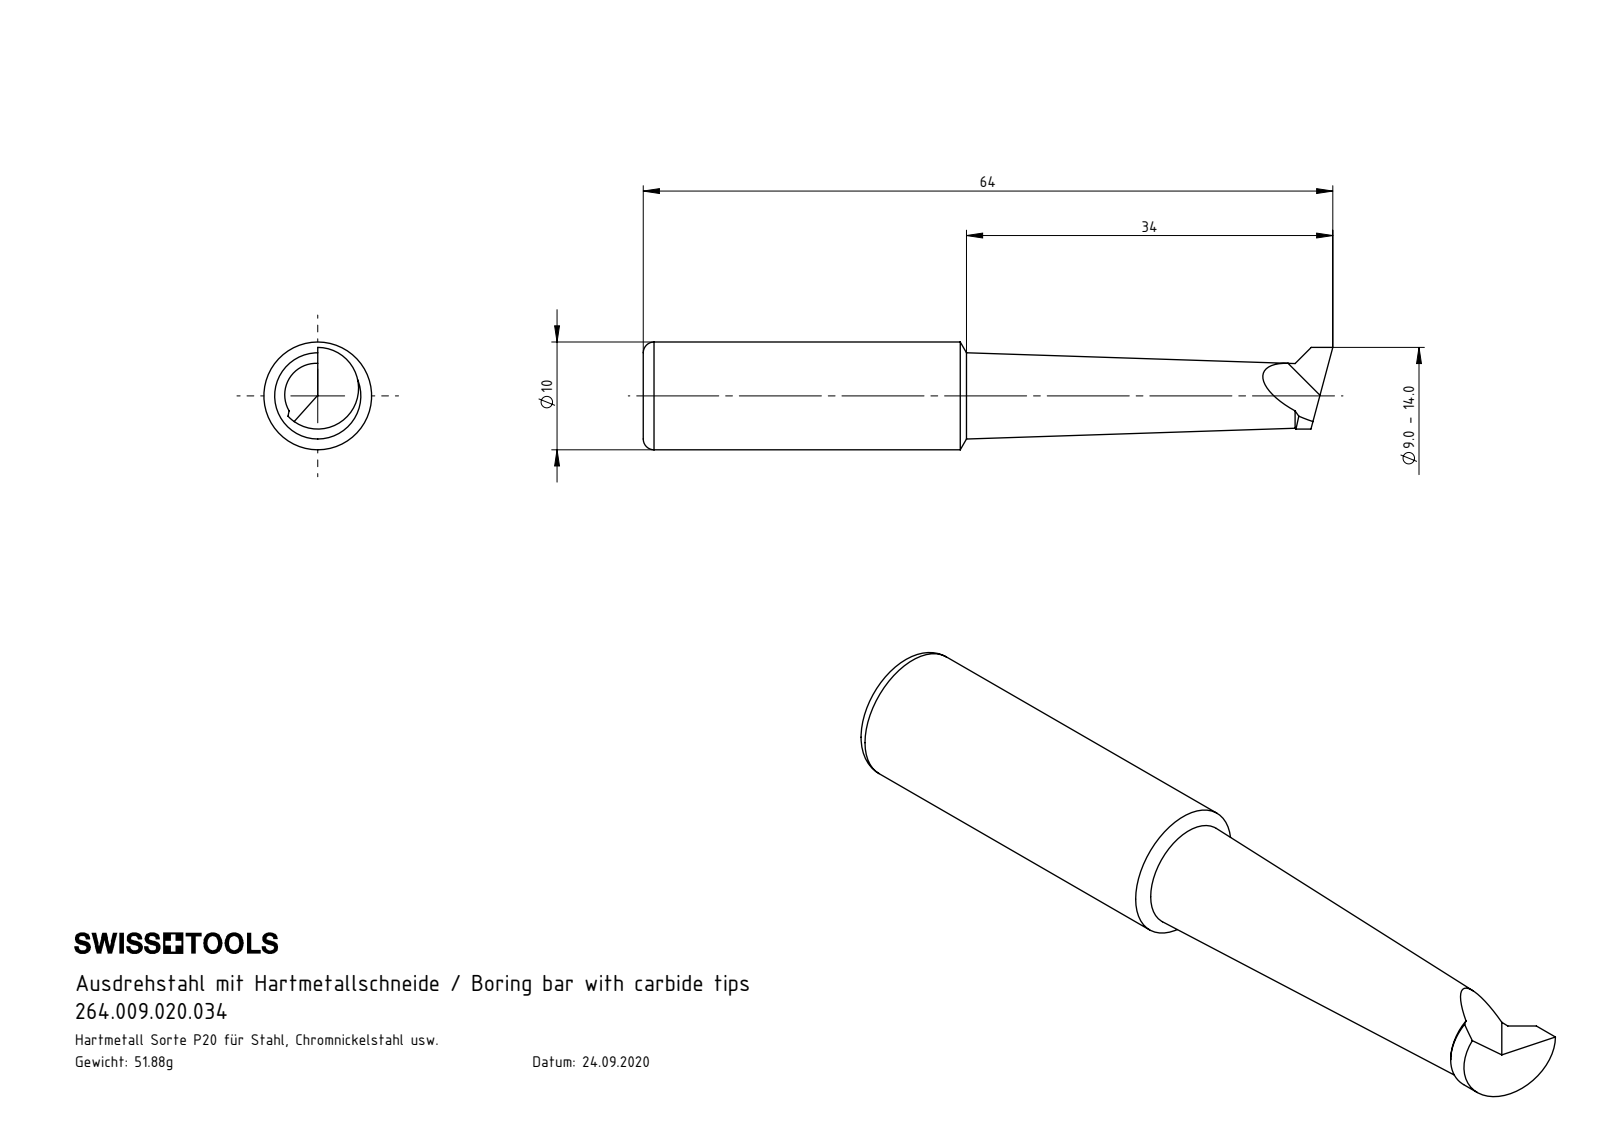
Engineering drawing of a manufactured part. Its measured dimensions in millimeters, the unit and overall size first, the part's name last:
Units: millimetres
Overall size (bounding box): 64 × 10 × 10
Round bosses / shafts (diameter × count): ⌀10 ×1
Partial cylindrical surfaces — rounded edges, fillets, slot ends (radius × count): R3.79 ×1
Volume: 3 578 mm³ · Surface area: 1 776 mm²
Bodies: 1 solid, 10 faces (4 planar, 2 cylindrical, 4 other)
Part name (STEP PRODUCT): U10.B09.002.034
STEP written by: SolidWorks 2017 (AUTOMOTIVE_DESIGN)
